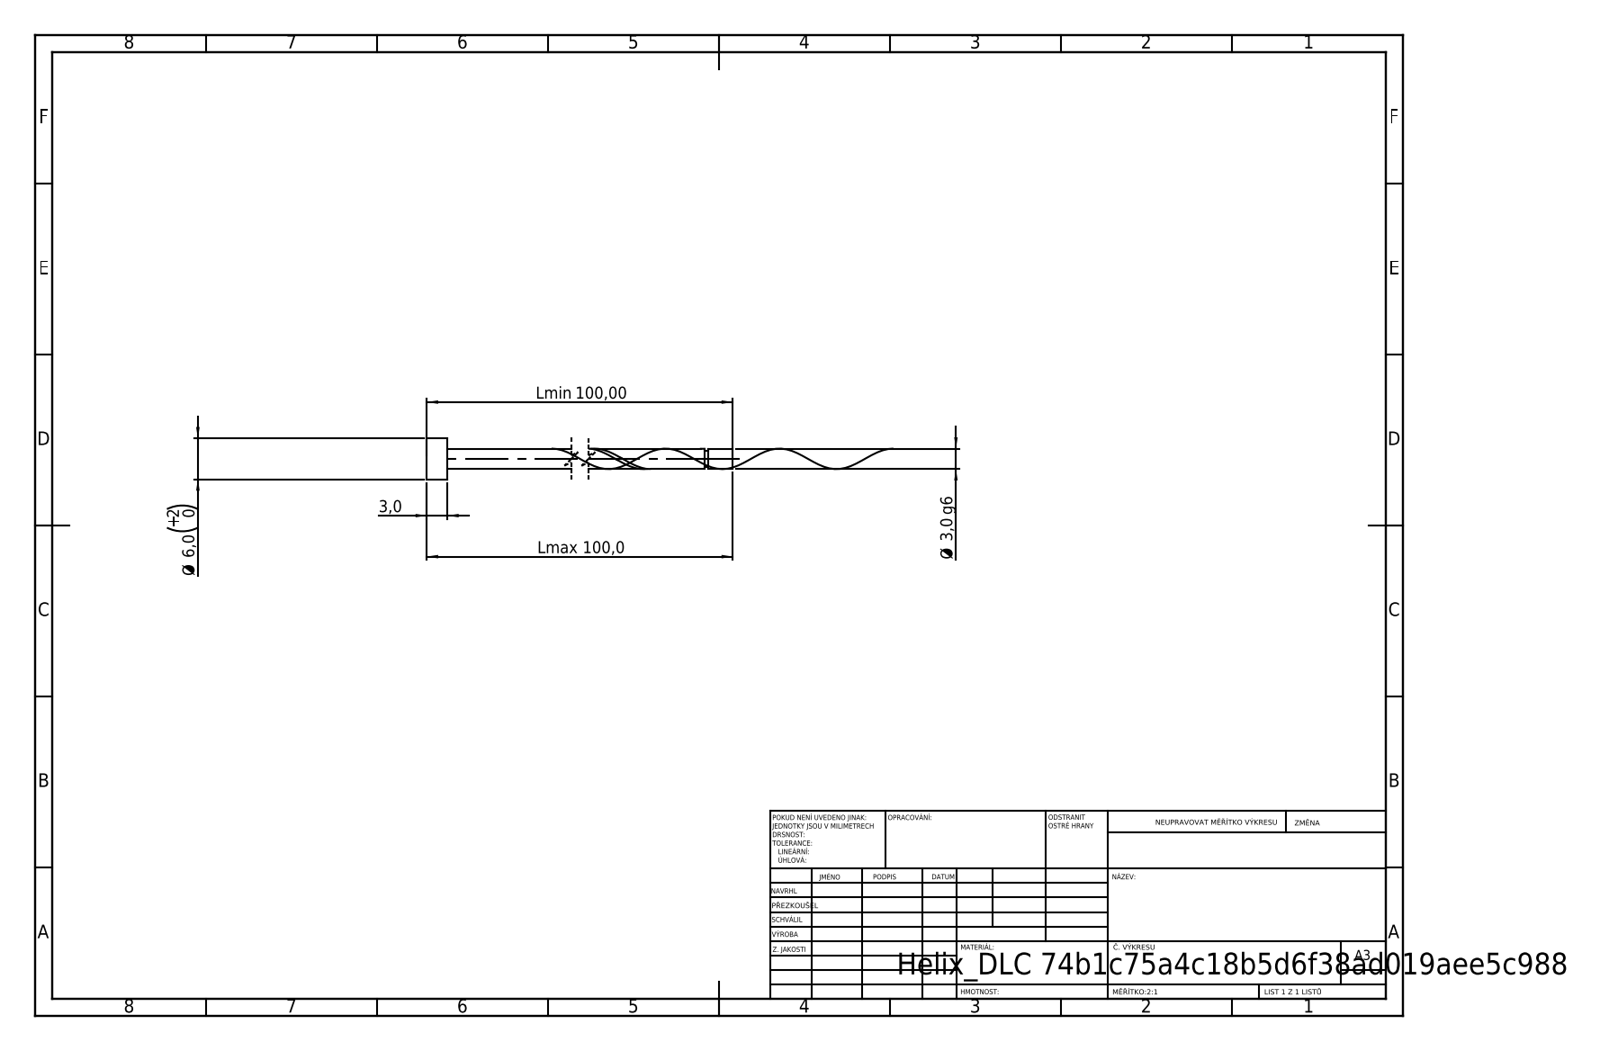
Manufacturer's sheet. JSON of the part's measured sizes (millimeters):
{"step_written_by": "SolidWorks 2019 (CONFIG_CONTROL_DESIGN)", "units": "millimeters", "bodies": {"solids": 1, "faces": 21, "planar": 6, "cylindrical": 14, "other": 1}, "overall_size": [100, 6, 6], "volume_mm3": 762, "surface_area_mm2": 1048, "round_bosses_or_shafts": [[6, 1], [3, 1], [2.4, 1]], "face_to_face_distances": [3, 100, 97, 96.46, 93.46, 3.54, 95.86, 92.86, 0.6, 4.14]}
